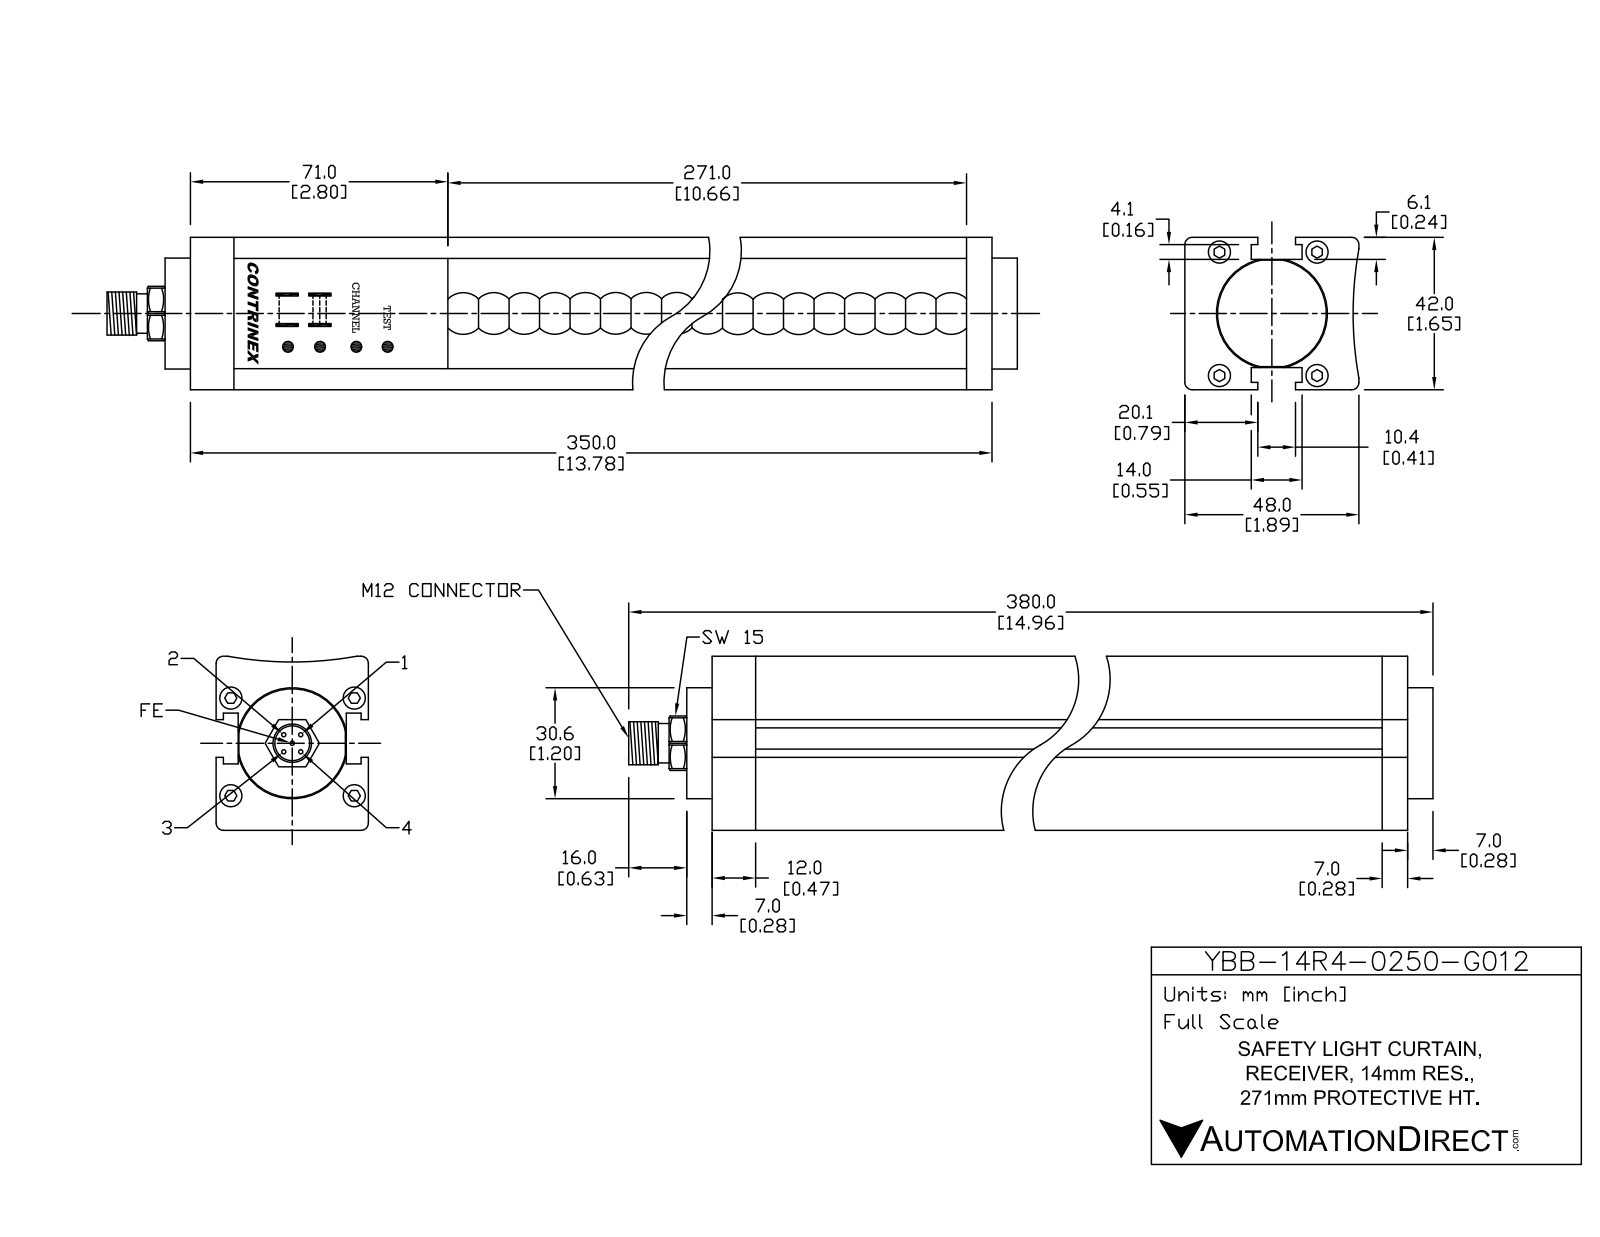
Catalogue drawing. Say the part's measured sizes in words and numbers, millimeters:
The part is named "YBB-14R4-0250-G012". Its 3-D file was written by "SolidWorks 2016 (AUTOMOTIVE_DESIGN)". It is 19 solids with 440 faces: 208 planar, 168 cylindrical and 64 other. Overall it measures 380 by 48 by 42 millimeters. Its volume is 637 190 cubic millimeters and its surface area 92 478 square millimeters. Round holes: 4 of diameter 6, 1 of diameter 8.5, 1 of diameter 32. Round bosses or shafts: 5 of diameter 1, 4 of diameter 5.5, 1 of diameter 30.6, 1 of diameter 12, 1 of diameter 10.5. Partial cylindrical surfaces (rounded edges, fillets, slot ends): 48 of radius 1, 4 of radius 0.5, 2 of radius 0.55, 1 of radius 8.2, 1 of radius 100. The main face-to-face distances are 6.3, 35.7, 42, 29.4, 330, 14, 17.2, 31.2, 8, 12. The hole center spacings are 21.04, 22.34, 26.9, 34, 43.35.
